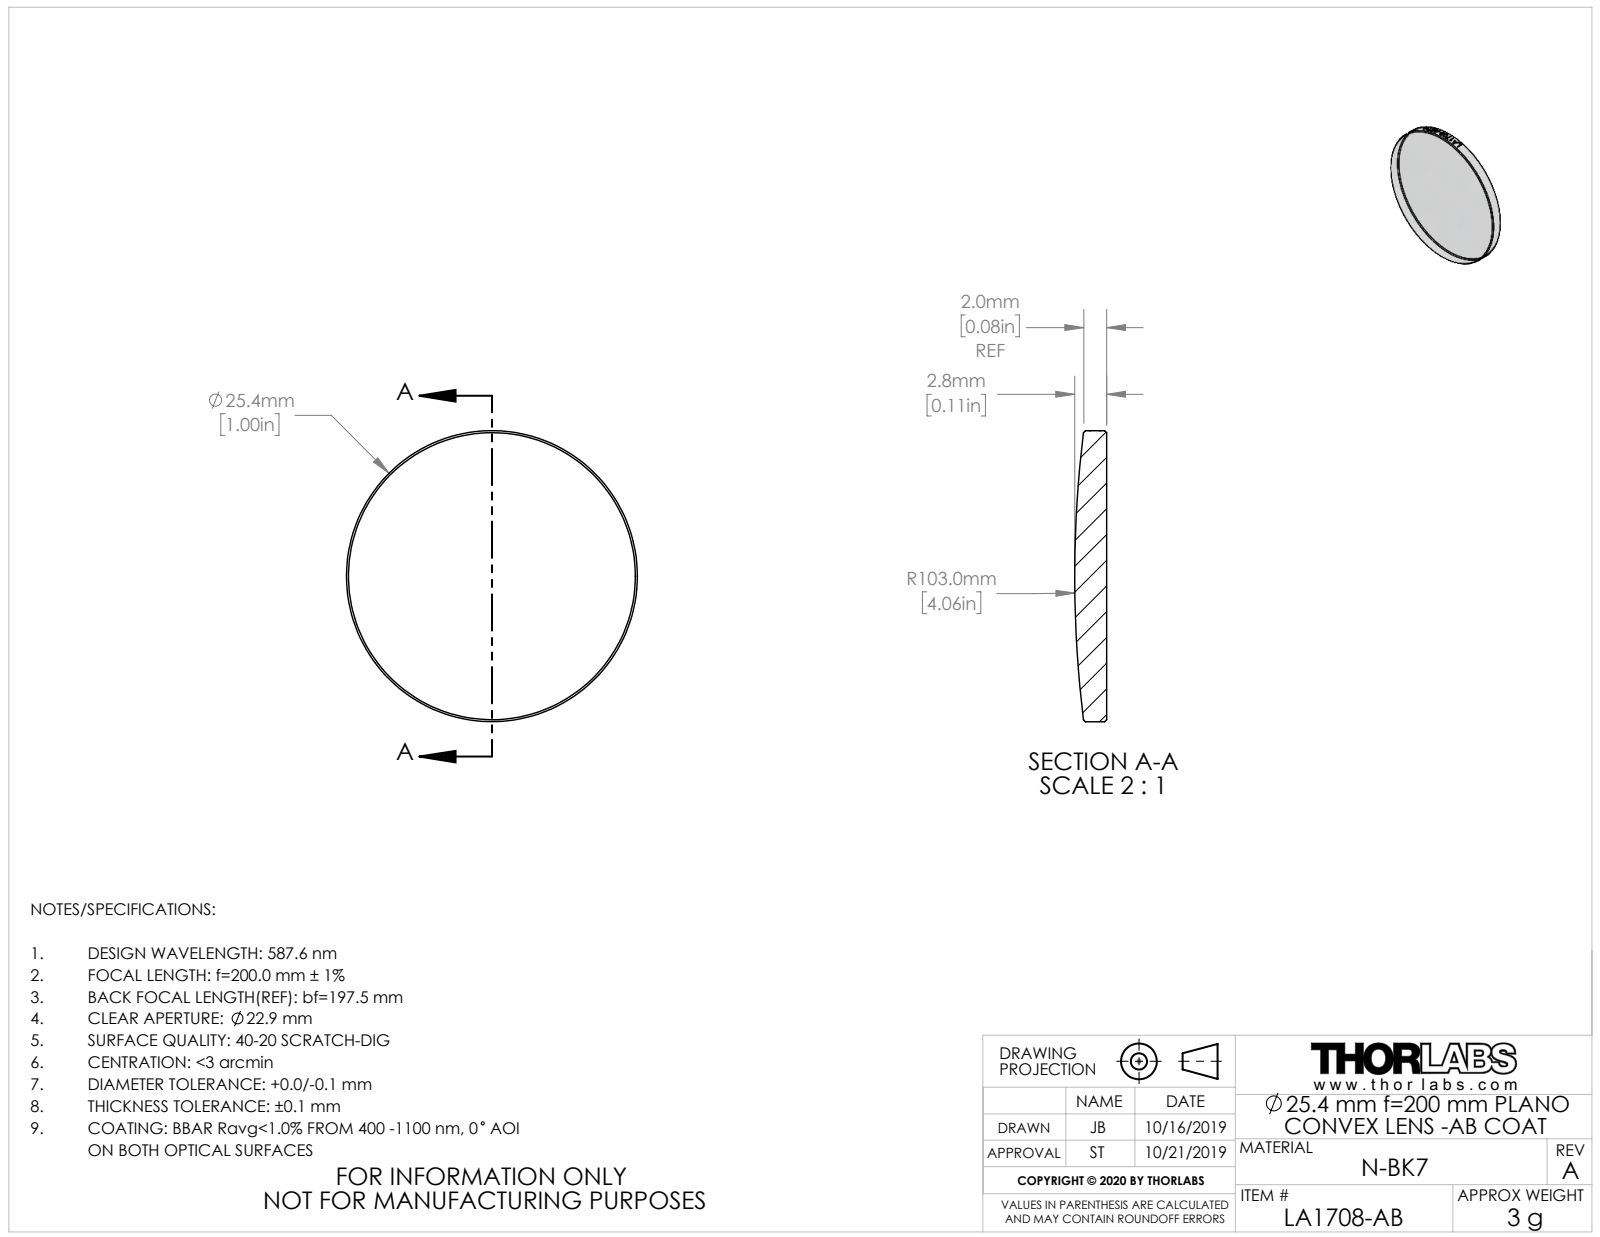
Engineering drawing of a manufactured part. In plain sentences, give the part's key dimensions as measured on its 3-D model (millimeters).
The part is named "TTN195775-E0W". Its 3-D file was written by "SolidWorks 2018 (CONFIG_CONTROL_DESIGN)". It is 1 solid with 29 faces: 1 planar, 22 cylindrical and 6 other. Overall it measures 25.4 by 25.4 by 2.8 millimeters. Its volume is 1 200 cubic millimeters and its surface area 1 159 square millimeters. Round bosses or shafts: 1 of diameter 25.4.
